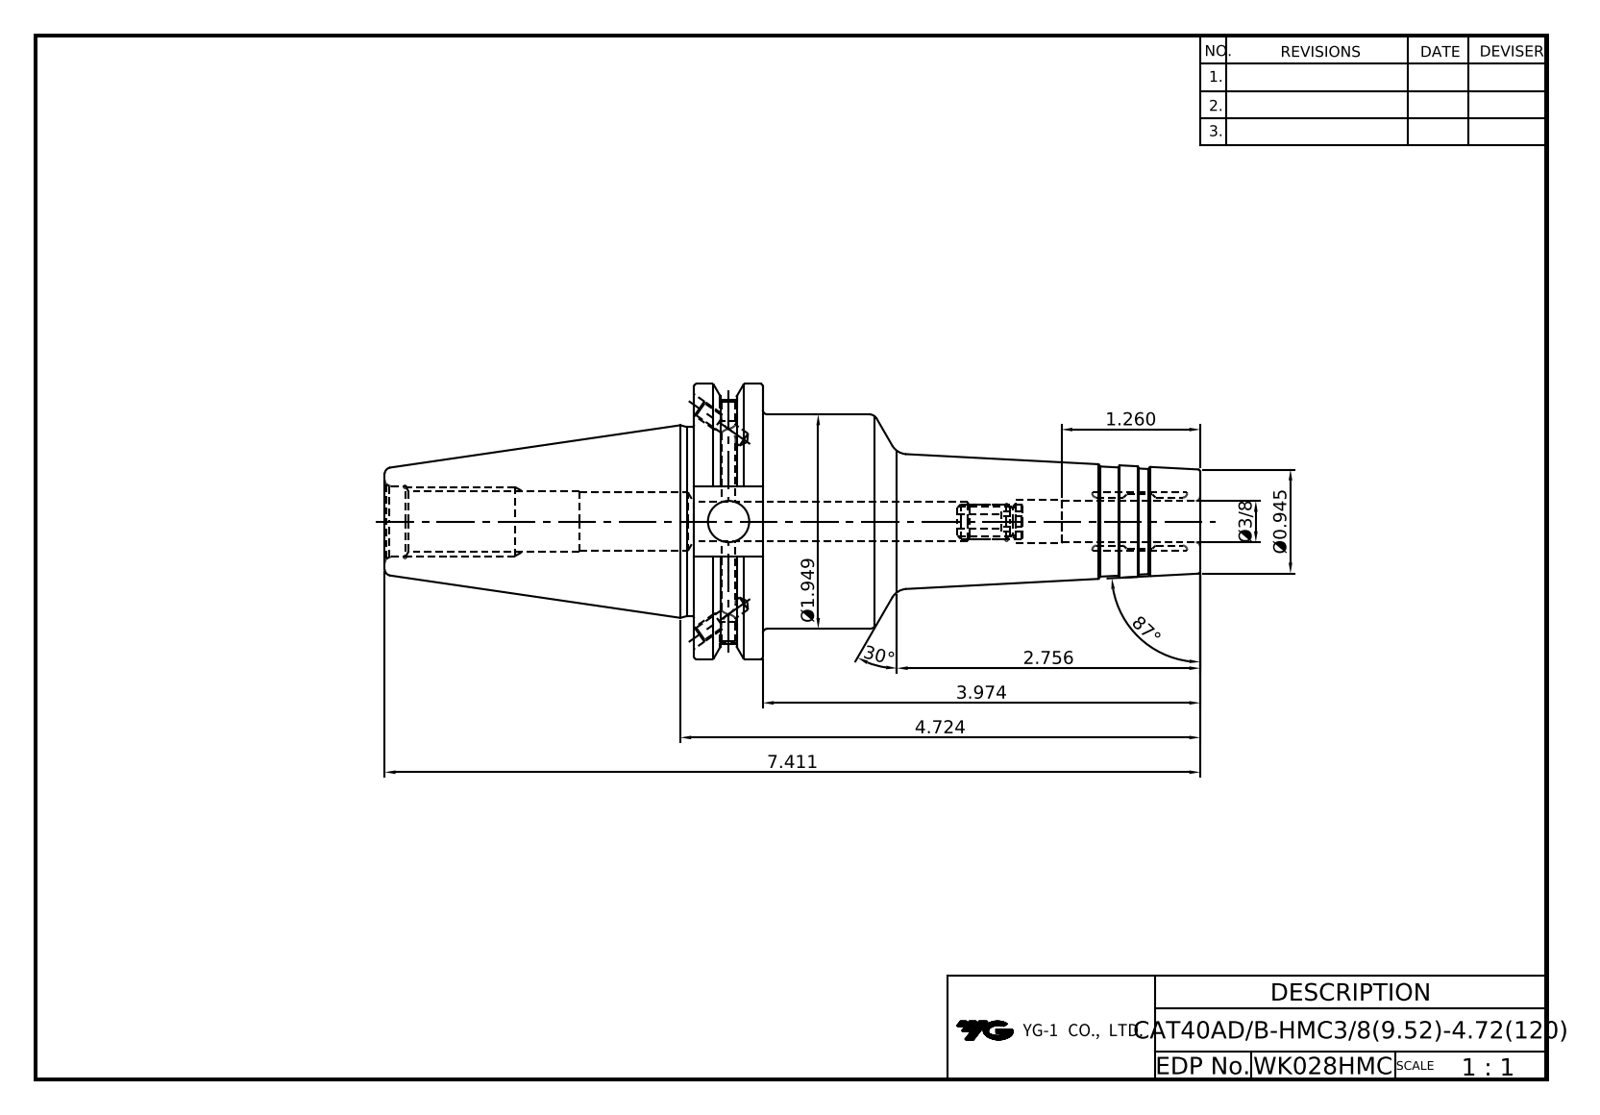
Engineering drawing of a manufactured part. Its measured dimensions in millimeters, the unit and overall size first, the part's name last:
Units: millimetres
Overall size (bounding box): 188.25 × 63.5 × 60.84
Round holes (diameter × count): ⌀3.3 ×3, ⌀4 ×3, ⌀9.53 ×2, ⌀4.2 ×1, ⌀8 ×1, ⌀9 ×1, ⌀10 ×1, ⌀13.49 ×1, ⌀15.88 ×1, ⌀16.3 ×1
Round bosses / shafts (diameter × count): ⌀63.5 ×1, ⌀49.5 ×1, ⌀43.6 ×1
Partial cylindrical surfaces — rounded edges, fillets, slot ends (radius × count): R8.19 ×1, R28.15 ×1
Main face-to-face distances: 15.88, 116.83, 100.95, 47.6, 16.38, 71.42, 87.3, 188.25, 6, 77.47
Volume: 193 103 mm³ · Surface area: 35 703 mm²
Bodies: 1 solid, 168 faces (47 planar, 61 cylindrical, 60 other)
Part name (STEP PRODUCT): CAT40ADB_90_20200821
STEP written by: CREO PARAMETRIC BY PTC INC, 2018400 (CONFIG_CONTROL_DESIGN)
